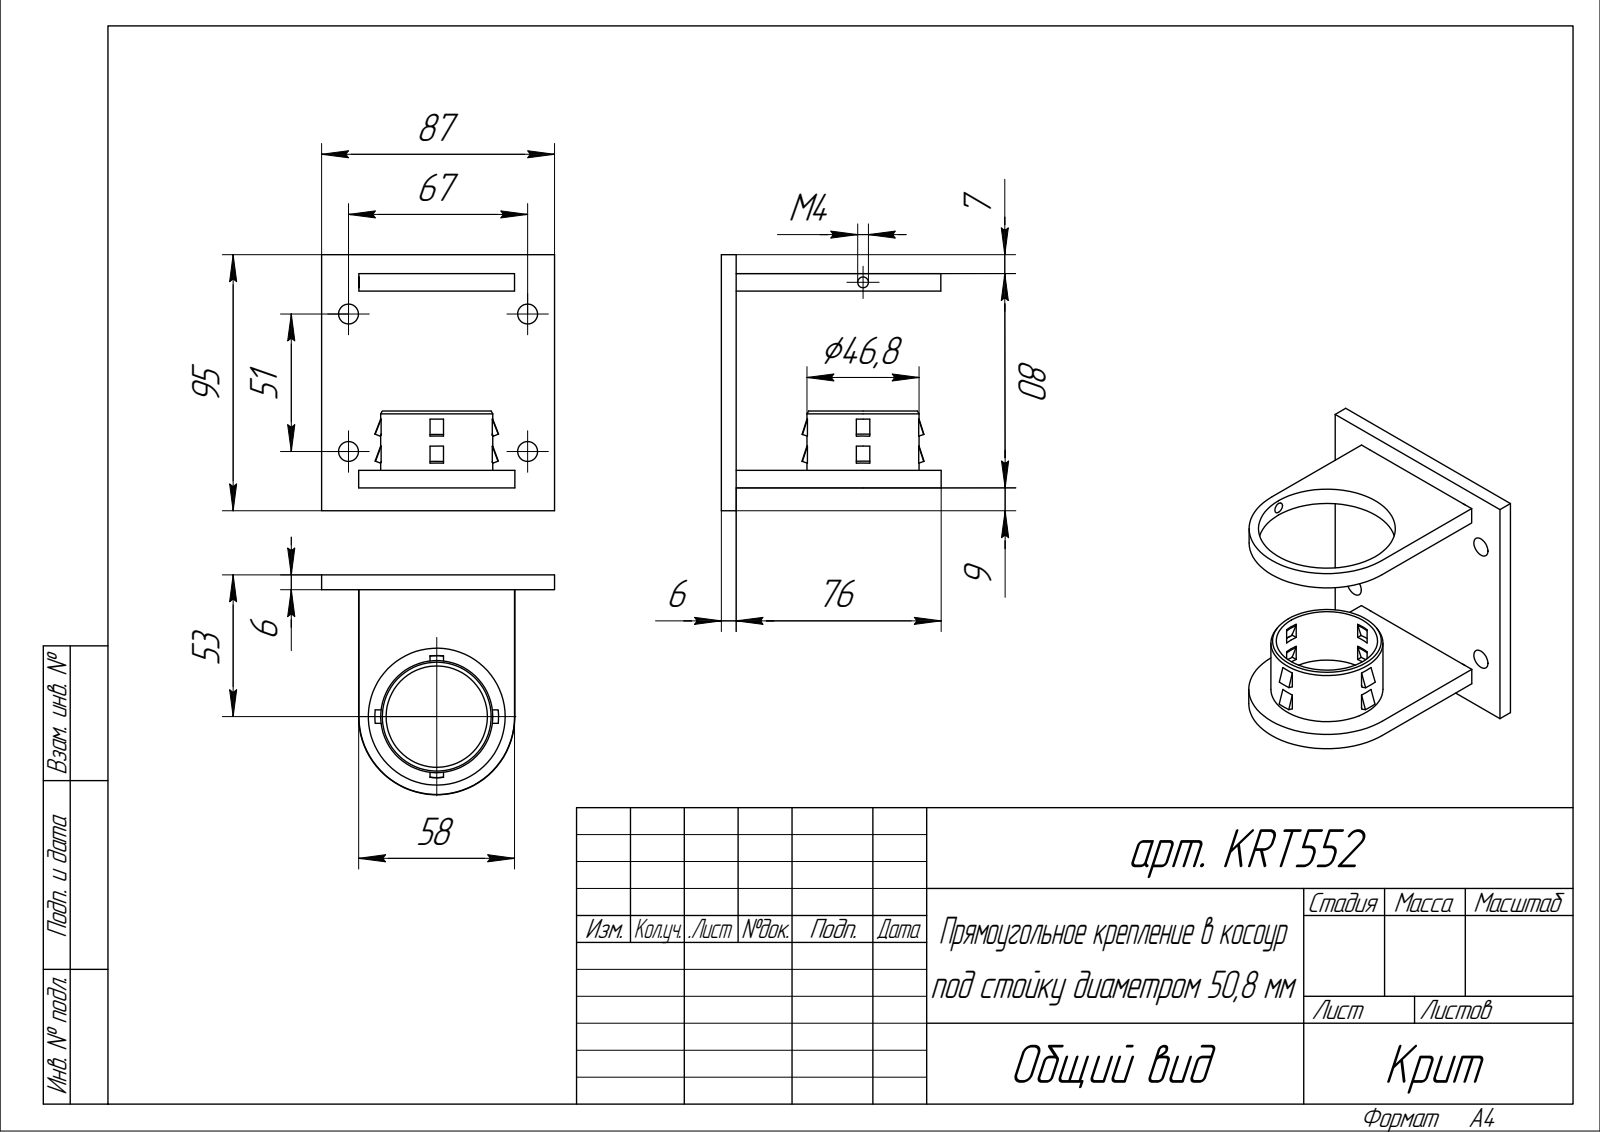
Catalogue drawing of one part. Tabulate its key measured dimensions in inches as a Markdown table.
| quantity | value |
| --- | --- |
| part name | Сборка; Деталь |
| STEP written by | ASCON Math Kernel (AUTOMOTIVE_DESIGN) |
| units | inches |
| bodies | 3 solids, 125 faces (98 planar, 26 cylindrical, 1 other) |
| overall size | 3.74 × 3.406 × 3.213 |
| volume | 5.407 in³ |
| surface area | 64.93 in² |
| round holes (diameter × count) | 0.291 × 4, 0.157 × 1, 1.48 × 1, 2 × 1 |
| round bosses / shafts (diameter × count) | 1.638 × 1 |
| partial cylindrical surfaces (radius × count) | 0.74 × 8, 0.819 × 8, 1.138 × 1, 1.142 × 1 |
| main face-to-face distances | 0.217, 0.256, 2.874, 3.13, 2.618, 3.406, 0.197, 0.02, 2.28, 2.283 |
| hole center spacings | 2.008, 2.618, 3.299 |
